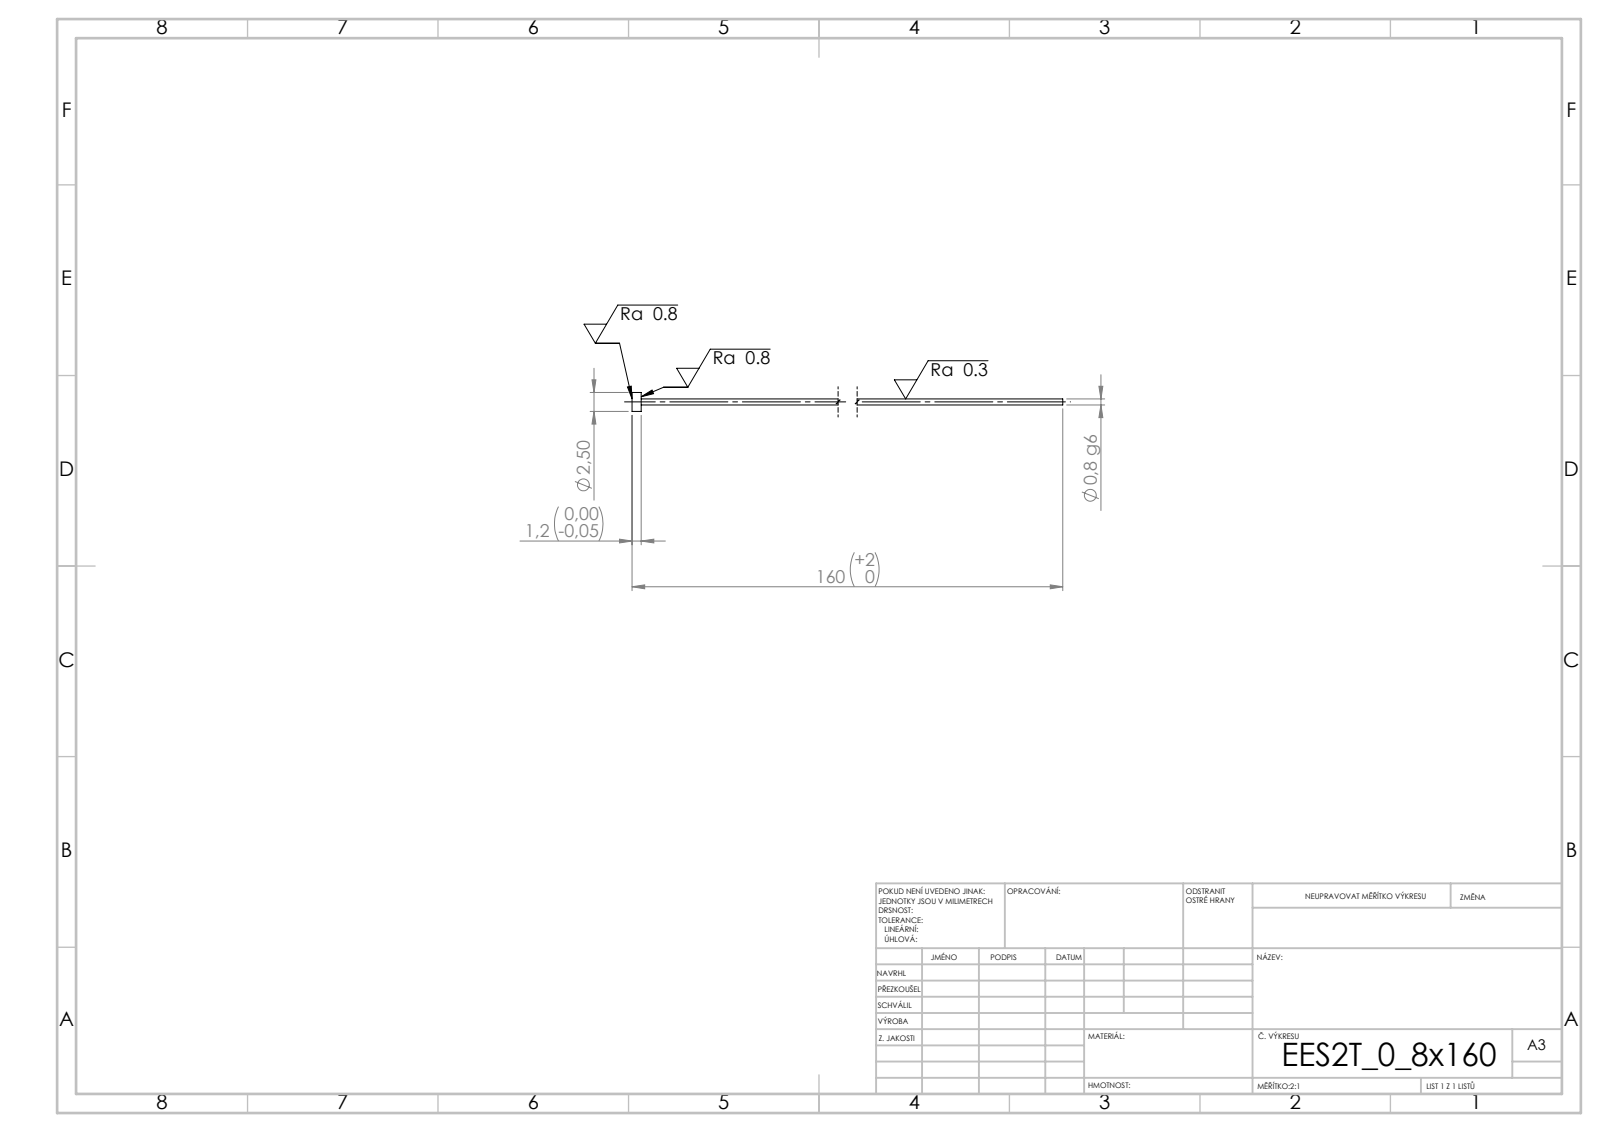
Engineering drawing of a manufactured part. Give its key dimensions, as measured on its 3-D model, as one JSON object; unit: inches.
{"step_written_by": "SolidWorks 2019 (CONFIG_CONTROL_DESIGN)", "units": "inches", "bodies": {"solids": 1, "faces": 7, "planar": 3, "cylindrical": 4, "other": 0}, "overall_size": [6.299, 0.098, 0.098], "volume_in3": 0.005, "surface_area_in2": 0.648, "round_bosses_or_shafts": [[0.098, 1], [0.031, 1]], "face_to_face_distances": [0.047, 6.299, 6.252]}
